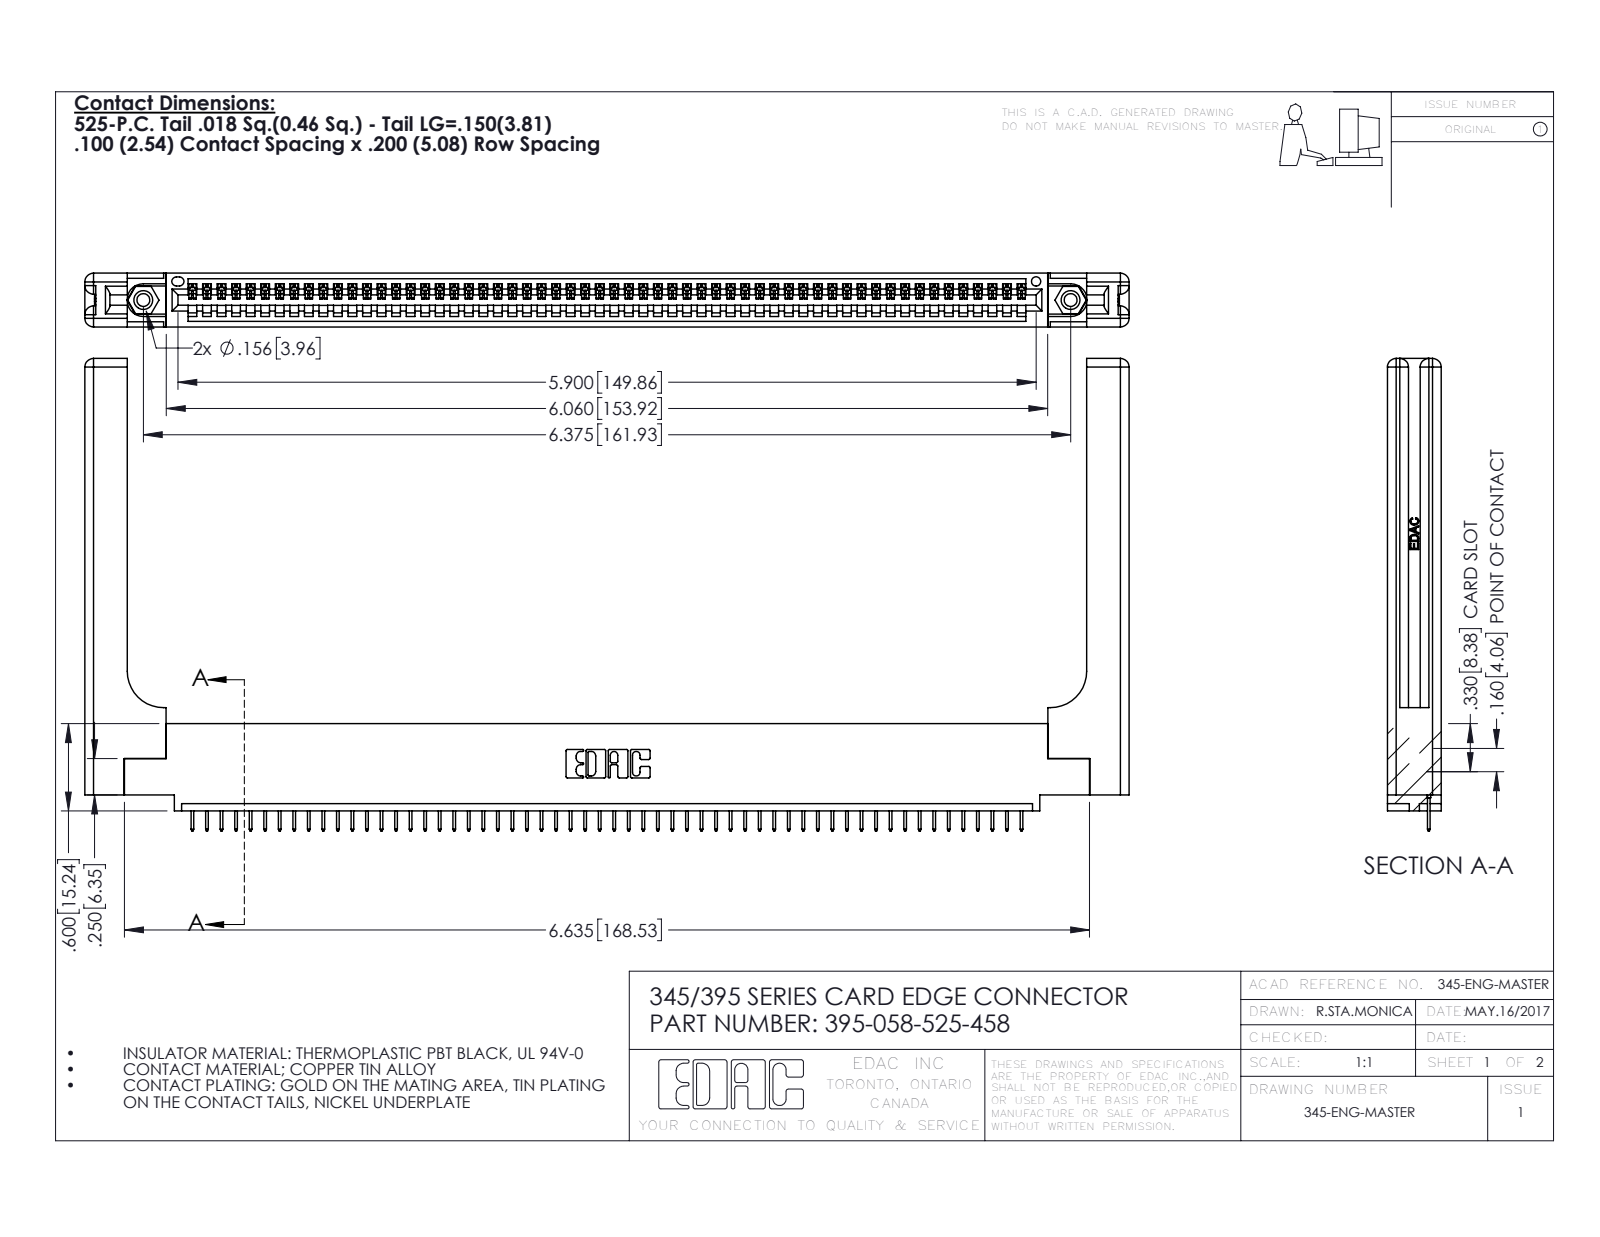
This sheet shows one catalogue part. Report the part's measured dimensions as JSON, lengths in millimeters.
{"part_name": "395-058-525-458; 345-220-058_345-220-058; 345 Part_0.110 Offset - 0.156 Dia-TH; 345-292-001_345-293-125 (+1 more)", "step_written_by": "SolidWorks 2020 (CONFIG_CONTROL_DESIGN)", "units": "millimeters", "bodies": {"solids": 63, "faces": 3982, "planar": 2900, "cylindrical": 1022, "other": 60}, "overall_size": [182.3, 82.5, 9.4], "volume_mm3": 25650, "surface_area_mm2": 27590, "round_holes": [[2.3, 2], [3.2, 2], [4, 2], [1.6, 1]], "round_bosses_or_shafts": [[3.9, 2]], "partial_cylinders_radius": [[0.2, 116], [0.3, 22], [1.5, 16], [0.2, 6], [0.8, 6], [0.7, 3], [0.8, 2], [0.8, 2]], "face_to_face_distances": [9.4, 1.8, 7.6, 2.5, 6.9, 0.6, 5.1, 5.7, 3.8, 3.8], "hole_center_spacings": [6.9, 155.9, 161.9]}
